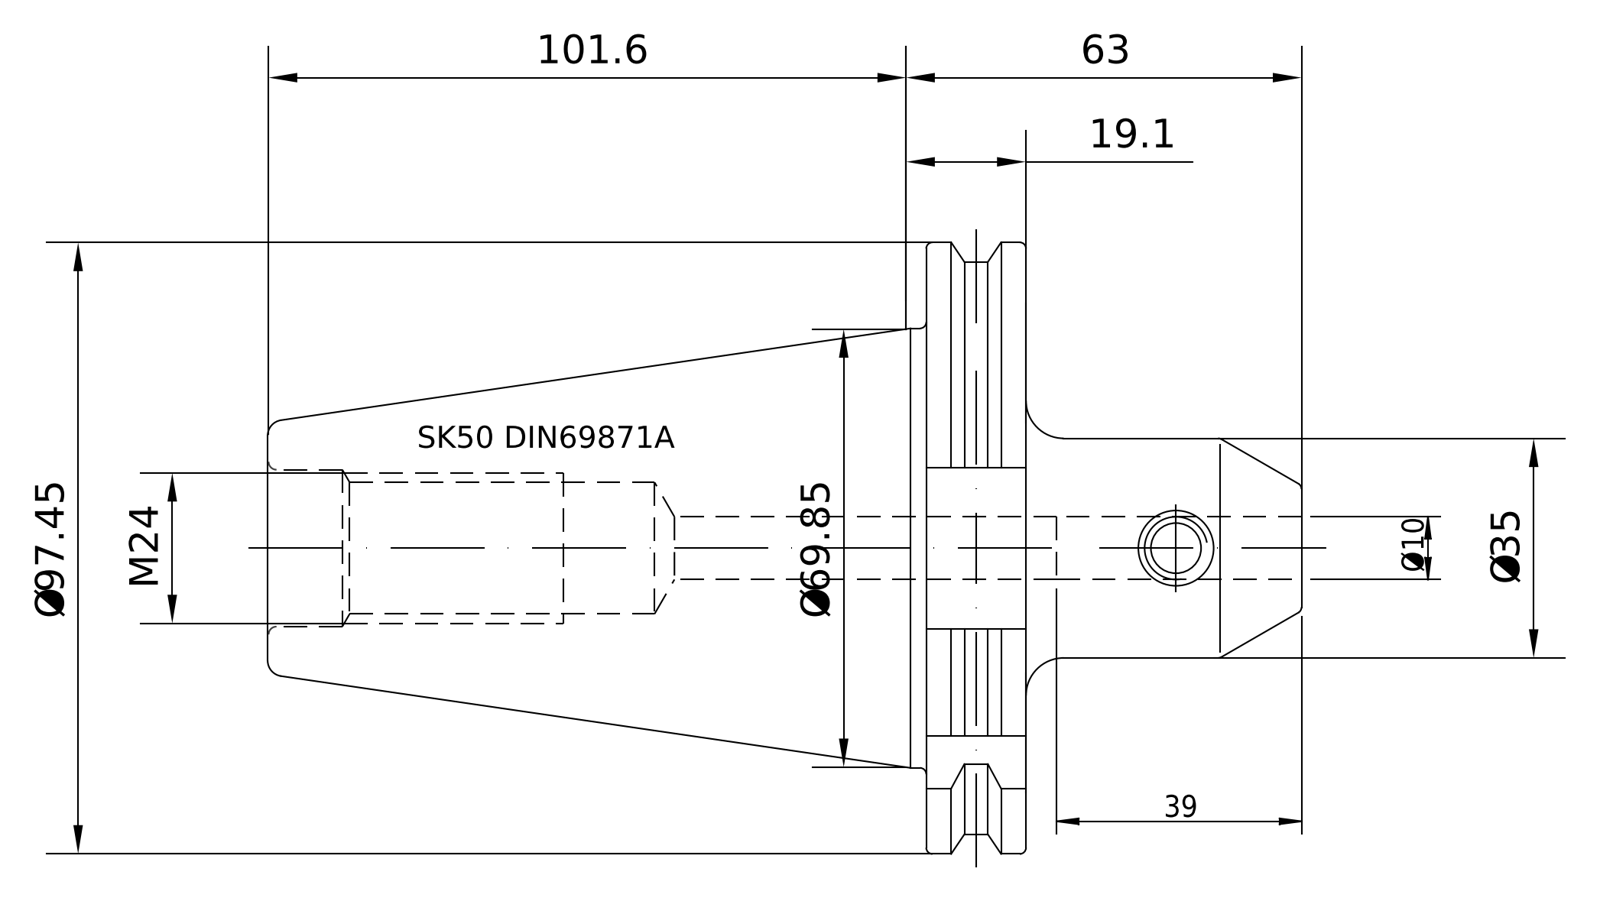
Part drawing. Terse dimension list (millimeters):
name: 50-300-10
written by: PRO/ENGINEER BY PARAMETRIC TECHNOLOGY CORPORATION, 2010430 (CONFIG_CONTROL_DESIGN)
unit: mm
bodies: 1 solid, 103 faces (21 planar, 32 cylindrical, 50 other)
size: 164.6 × 97.47 × 94
volume: 374 180 mm³; area: 48 274 mm²
holes: 2× ⌀10, 1× ⌀8.5, 1× ⌀20.75, 1× ⌀25.01, 1× ⌀25.7
bosses: 1× ⌀91, 1× ⌀69.15, 1× ⌀35, 1× ⌀24.01
rounds: 5× R1.75, 1× R48.74
face distances: 15.85, 104.8, 120.65, 72.8, 25.8, 164.6, 59.8, 43.95, 48, 56.8
